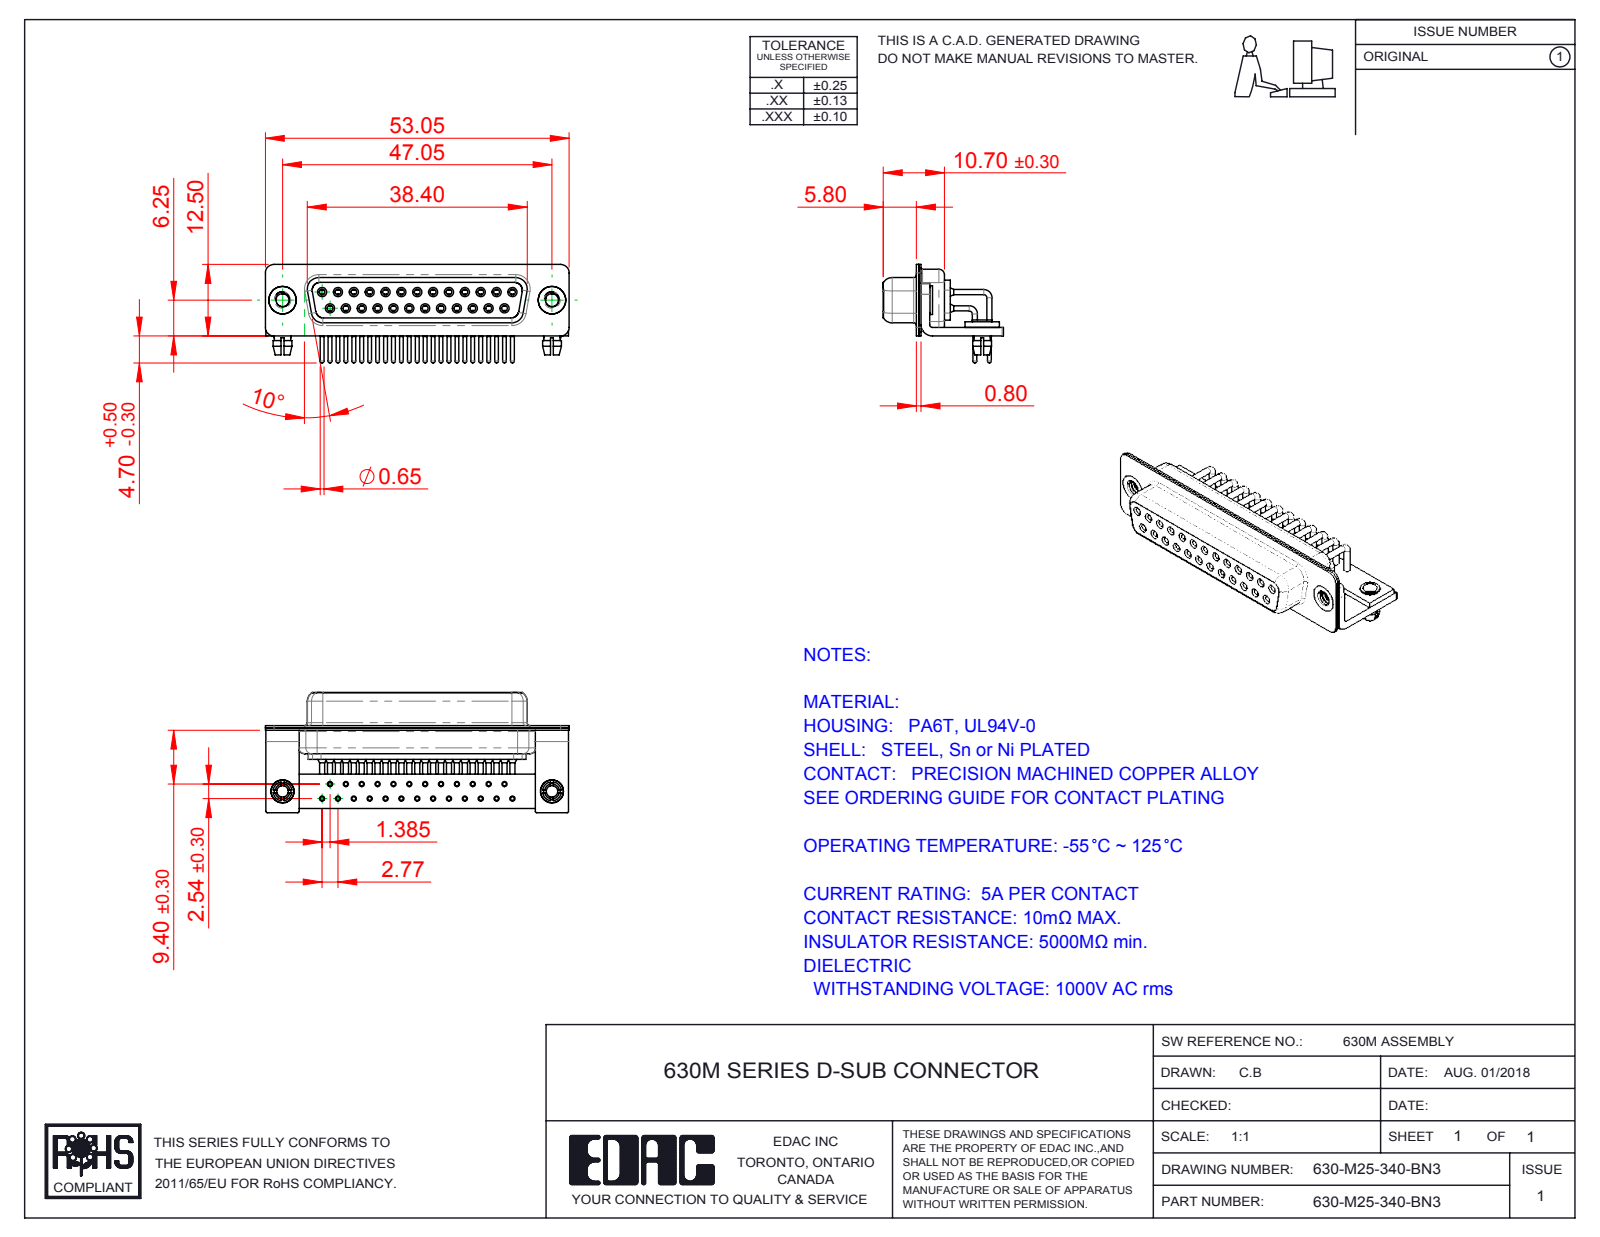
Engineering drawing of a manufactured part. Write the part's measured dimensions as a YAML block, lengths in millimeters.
part_name: "630M Shell Front_25 Contacts; 630-M25-340-BN3; 630M Contact Row 2; 630M Shell Rear_25 Contacts (+6 more)"
step_written_by: "SolidWorks 2016 (CONFIG_CONTROL_DESIGN)"
units: millimeters
bodies: {solids: 35, faces: 1796, planar: 516, cylindrical: 816, other: 464}
overall_size: [53.05, 21, 17.2]
volume: 4497
surface_area: 11342
round_holes:
  - {diameter: 2, count: 27}
  - {diameter: 0.9, count: 25}
  - {diameter: 1, count: 25}
  - {diameter: 1.1, count: 25}
  - {diameter: 1.7, count: 25}
  - {diameter: 1.8, count: 25}
  - {diameter: 2.26, count: 2}
  - {diameter: 2.5, count: 2}
  - {diameter: 3.2, count: 2}
  - {diameter: 4, count: 2}
  - {diameter: 4.8, count: 2}
round_bosses_or_shafts:
  - {diameter: 1.6, count: 25}
  - {diameter: 1.5, count: 25}
  - {diameter: 0.9, count: 25}
  - {diameter: 0.65, count: 25}
  - {diameter: 5, count: 2}
  - {diameter: 4.9, count: 2}
  - {diameter: 4, count: 2}
  - {diameter: 3.4, count: 2}
partial_cylinders:
  - {radius: 0.25, count: 16}
  - {radius: 1.5, count: 16}
  - {radius: 2, count: 13}
  - {radius: 1.35, count: 10}
  - {radius: 1.6, count: 8}
  - {radius: 0.5, count: 5}
  - {radius: 0.6, count: 4}
  - {radius: 0.65, count: 4}
face_to_face_distances: [0.4, 2.3, 1.9, 9.35, 1.45, 8.95, 0.85, 0.8, 6.2, 1]
hole_center_spacings: [2.77, 5.54, 8.31, 11.08, 13.85, 3.16, 4.87, 16.62]
